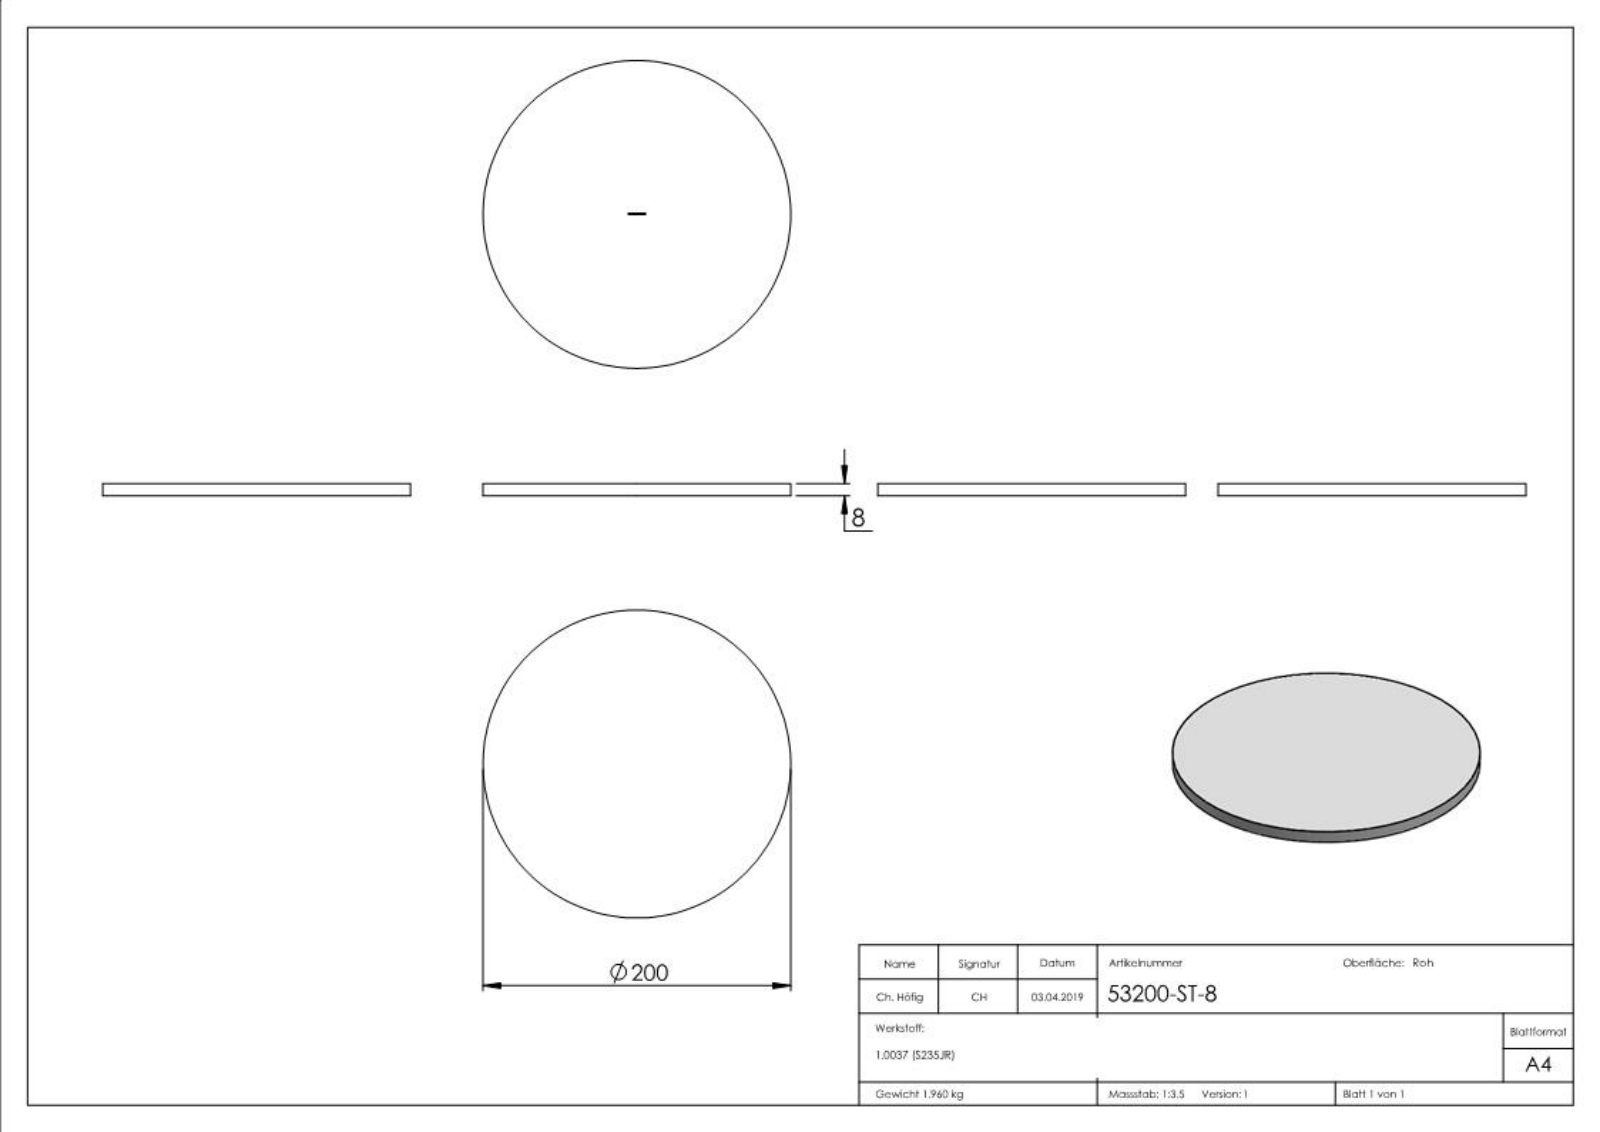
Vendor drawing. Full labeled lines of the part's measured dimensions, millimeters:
Part name (STEP PRODUCT): 53200-ST-8
STEP written by: SolidWorks 2015 (CONFIG_CONTROL_DESIGN)
Units: millimetres
Bodies: 1 solid, 242 faces (114 planar, 2 cylindrical, 126 other)
Overall size (bounding box): 200 × 200 × 8
Volume: 251 327 mm³ · Surface area: 67 864 mm²
Round bosses / shafts (diameter × count): ⌀200 ×1
Main face-to-face distances: 8, 7.9, 0.44, 1.78, 0.79, 0.83, 0.76, 0.99, 0.67, 1.21
